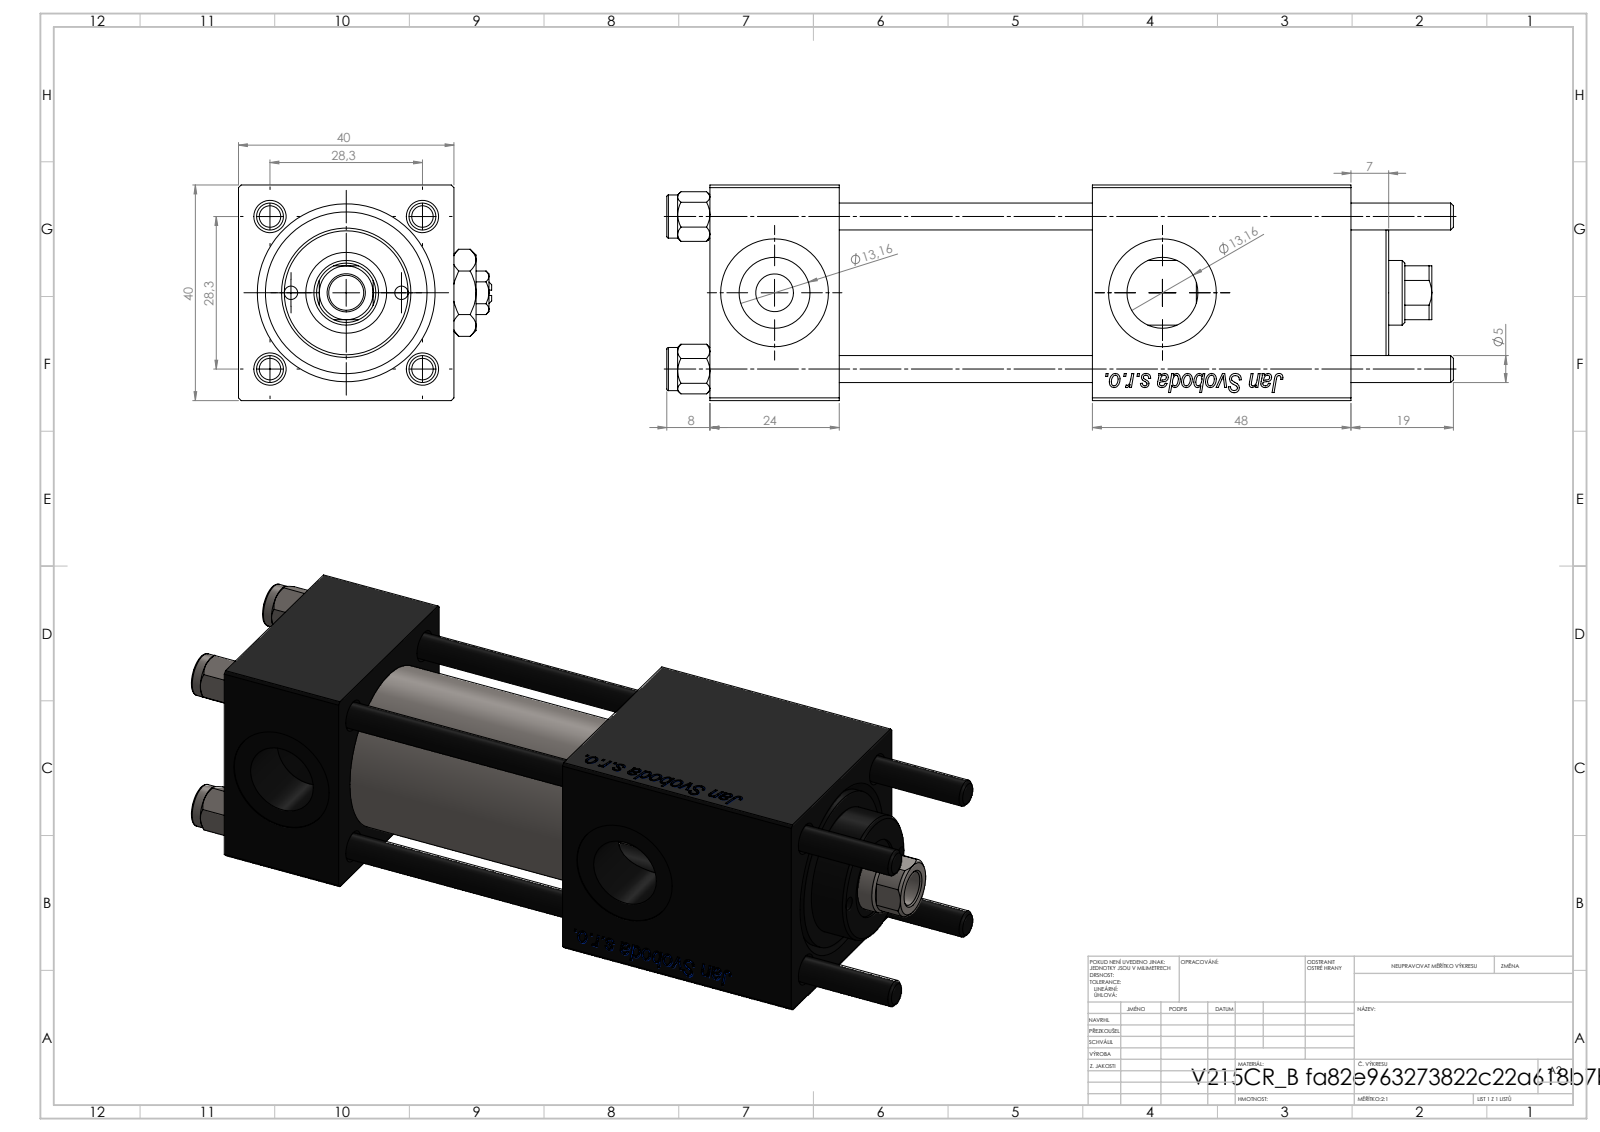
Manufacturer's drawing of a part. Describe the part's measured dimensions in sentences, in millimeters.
The part is named "Zatka_pro_OIL_PORT; V215_VC_A; V215CR_VCP_B; V215CR_B_TYCINKA (+2 more)". Its 3-D file was written by "SolidWorks 2019 (CONFIG_CONTROL_DESIGN)". It is 12 solids with 1209 faces: 455 planar, 86 cylindrical and 668 other. Overall it measures 146 by 47 by 40 millimeters. Its volume is 144 116 cubic millimeters and its surface area 59 551 square millimeters. Round holes: 4 of diameter 5, 3 of diameter 20, 2 of diameter 2.5, 2 of diameter 7, 2 of diameter 13.16, 1 of diameter 6.5, 1 of diameter 12, 1 of diameter 15, 1 of diameter 25, 1 of diameter 30. Round bosses or shafts: 4 of diameter 8, 1 of diameter 31, 1 of diameter 24. Partial cylindrical surfaces (rounded edges, fillets, slot ends): 1 of radius 5.5. The main face-to-face distances are 40, 24, 90.3, 66.3, 47, 71, 19.3, 48, 119, 95. The hole center spacings are 14.68, 20.01, 28.21, 28.3, 10.25, 40.02, 20.5, 72.
